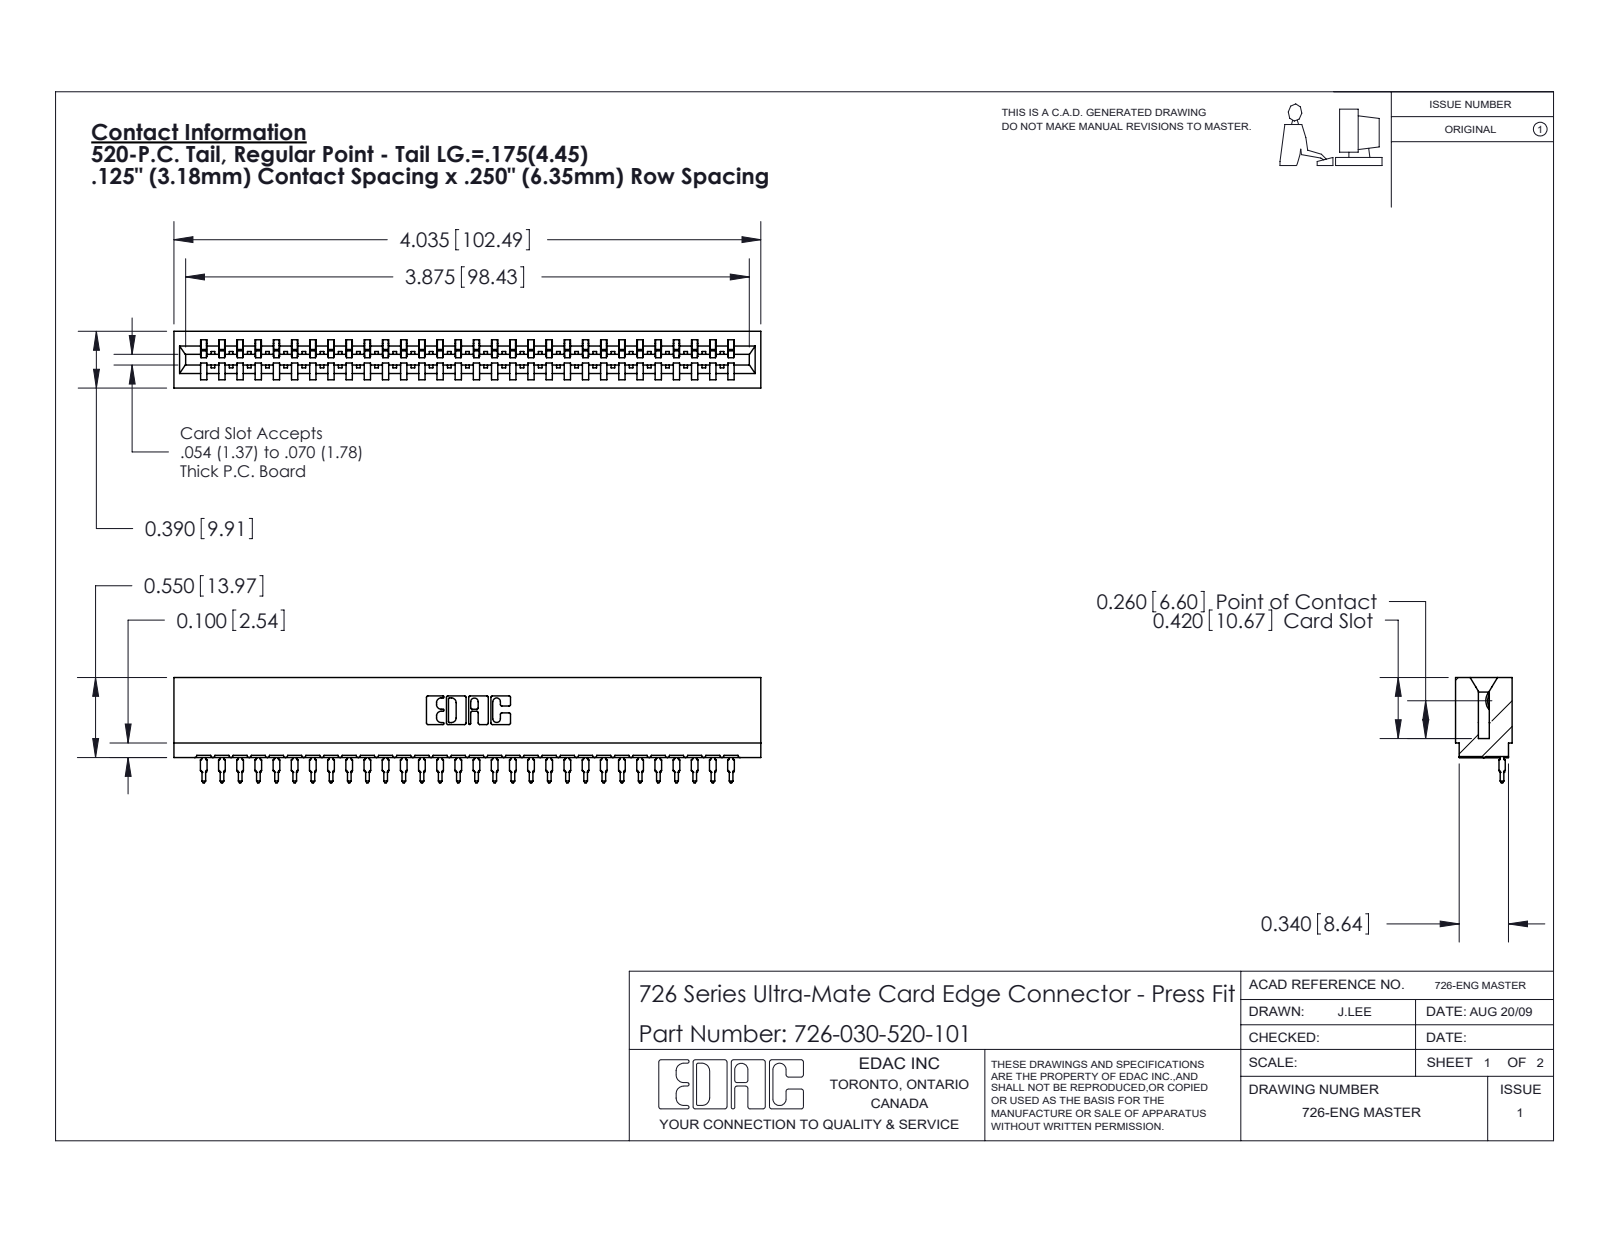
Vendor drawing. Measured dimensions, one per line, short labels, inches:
name: 746-292-001_520; 726-030-520-101; 726 Part_.515 Slot Depth - 01
written by: SolidWorks 2020 (CONFIG_CONTROL_DESIGN)
unit: in
bodies: 31 solids, 3337 faces (1945 planar, 612 cylindrical, 780 other)
size: 4.035 × 0.724 × 0.39
volume: 0.56 in³; area: 21.11 in²
rounds: 60× R0.021, 31× R0.015, 22× R0.01, 6× R0.007, 6× R0.031, 4× R0.005, 4× R0.011, 3× R0.026
face distances: 0.057, 0.333, 0.39, 0.25, 0.025, 0.307, 0.5, 0.75, 0.083, 0.275
